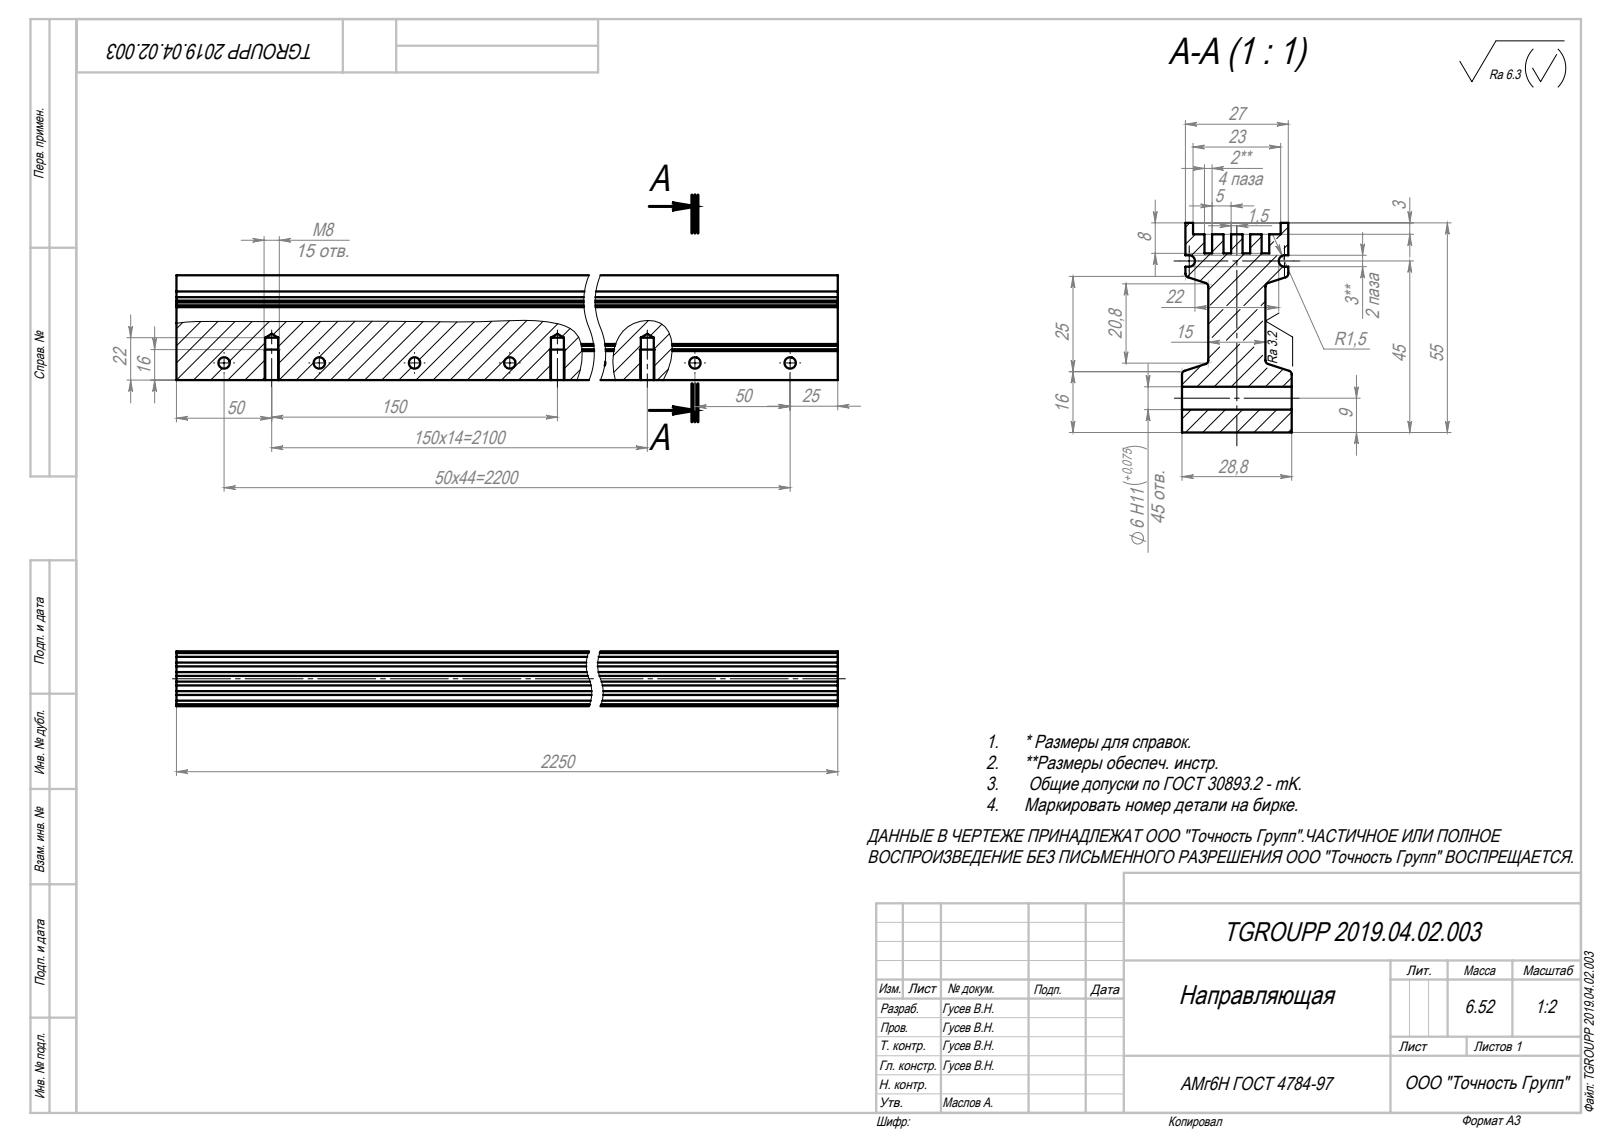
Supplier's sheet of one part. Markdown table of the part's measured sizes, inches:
| quantity | value |
| --- | --- |
| part name | TGROUPP 2019.04.02.003 |
| STEP written by | SolidWorks 2016 (AUTOMOTIVE_DESIGN) |
| units | inches |
| bodies | 1 solid, 201 faces (40 planar, 131 cylindrical, 30 other) |
| overall size | 88.583 × 2.165 × 1.134 |
| volume | 150.6 in³ |
| surface area | 873 in² |
| round holes (diameter × count) | 0.236 × 45, 0.268 × 15 |
| partial cylindrical surfaces (radius × count) | 0.039 × 8, 0.059 × 2 |
| main face-to-face distances | 0.197, 0.591, 0.394, 0.236, 0.272, 0.862, 0.118, 0.079, 0.276, 0.035 |
| hole center spacings | 5.906, 11.811, 17.717, 1.969, 23.622, 3.937, 7.874, 9.843 |
